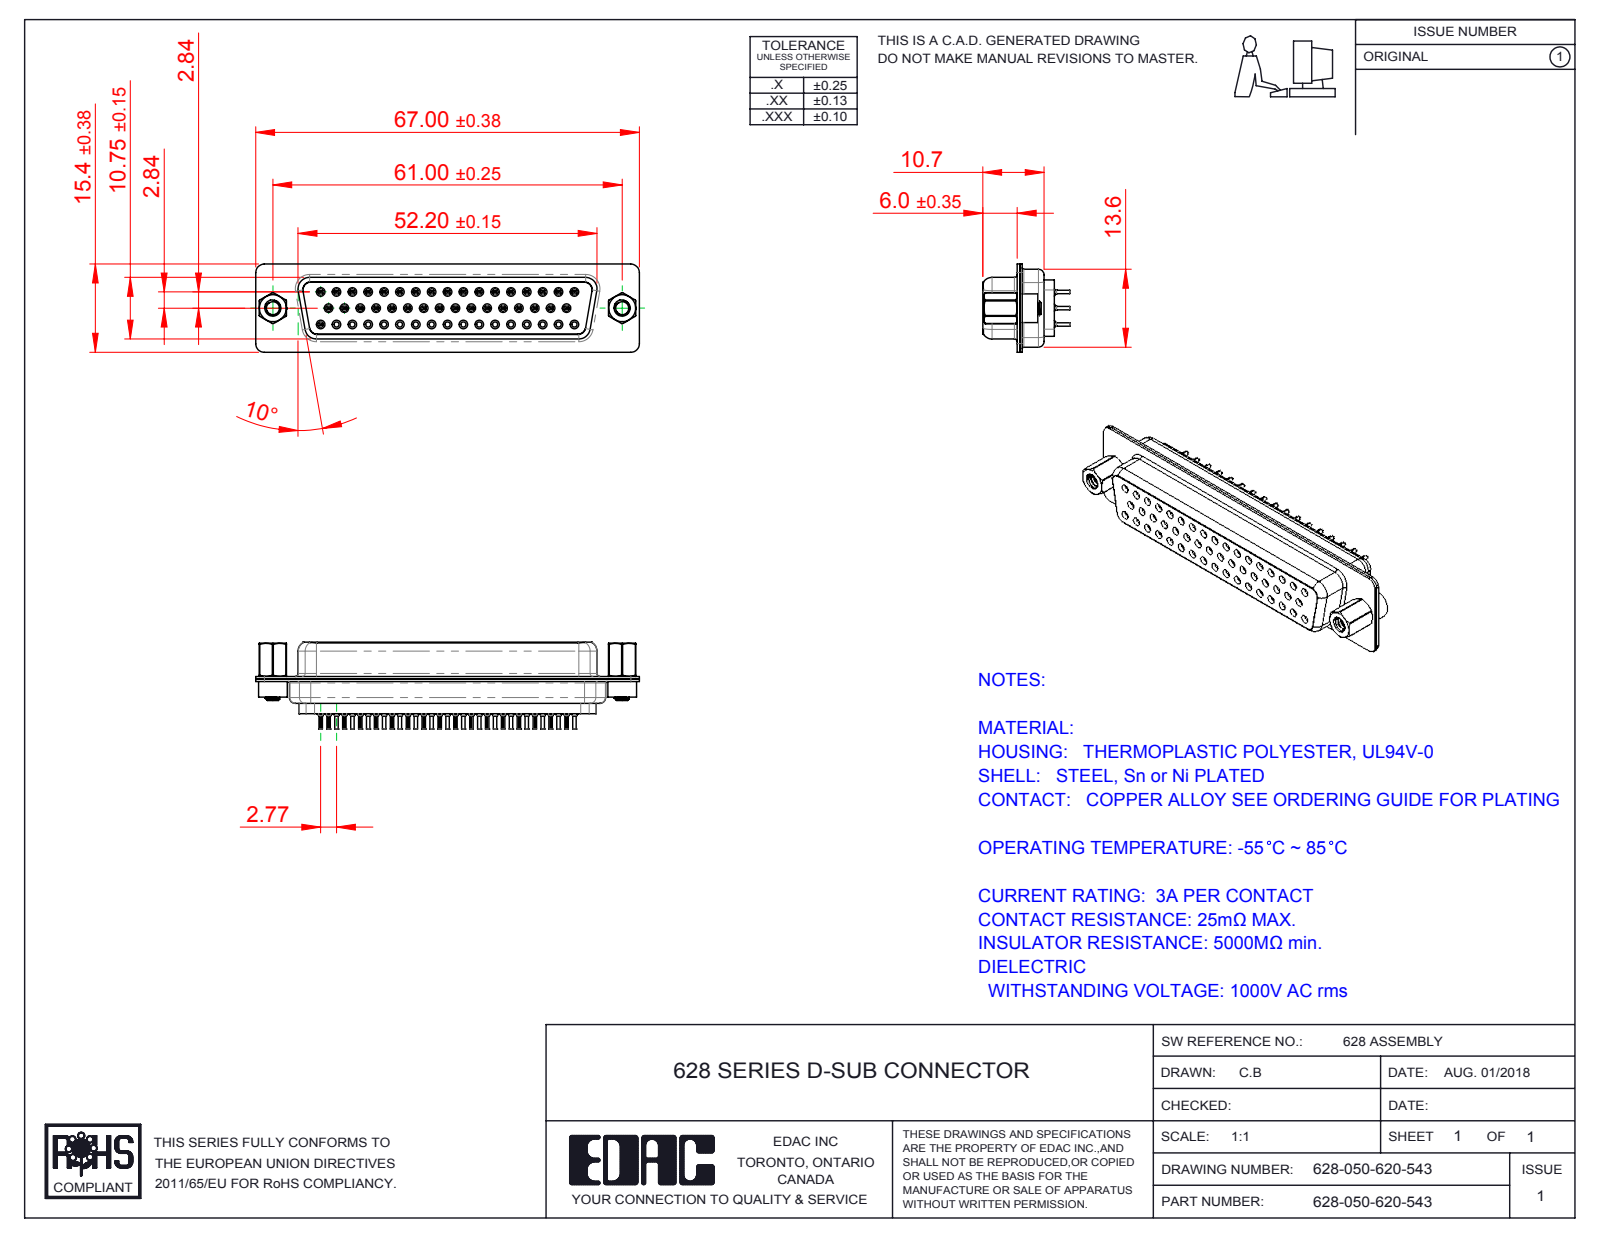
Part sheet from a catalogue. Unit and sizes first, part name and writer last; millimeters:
Units: millimetres
Overall size (bounding box): 67 × 15.4 × 15.2
Round holes (diameter × count): ⌀0.9 ×50, ⌀1.6 ×50, ⌀0.2 ×34, ⌀0.8 ×34, ⌀1.1 ×34, ⌀1.7 ×17, ⌀1.5 ×16, ⌀2 ×16, ⌀2.26 ×2, ⌀2.29 ×2, ⌀4 ×2, ⌀4.8 ×2
Round bosses / shafts (diameter × count): ⌀2 ×34, ⌀1.5 ×34, ⌀1.2 ×34, ⌀0.6 ×34, ⌀5 ×2, ⌀4.9 ×2, ⌀2.79 ×2
Partial cylindrical surfaces — rounded edges, fillets, slot ends (radius × count): R0.1 ×68, R0.28 ×33, R1.5 ×16, R2 ×12, R1.35 ×8, R0.25 ×4, R0.5 ×4, R0.6 ×4
Main face-to-face distances: 0.45, 0.4, 10.3, 0.9, 6.05, 6.5, 6.45, 6, 12.5, 11.33
Hole centre spacings: 3.16, 2.77, 5.54, 8.31, 11.08, 13.85, 16.62, 19.39
Volume: 6 794 mm³ · Surface area: 14 075 mm²
Bodies: 41 solids, 4931 faces (1191 planar, 1459 cylindrical, 2281 other)
Part name (STEP PRODUCT): 628 4-40 Threaded Rivet; 628 Shell Front_50 Contacts; 628 Contact Row 3_20L; 628 Housing_50 LP (+5 more)
STEP written by: SolidWorks 2016 (CONFIG_CONTROL_DESIGN)
